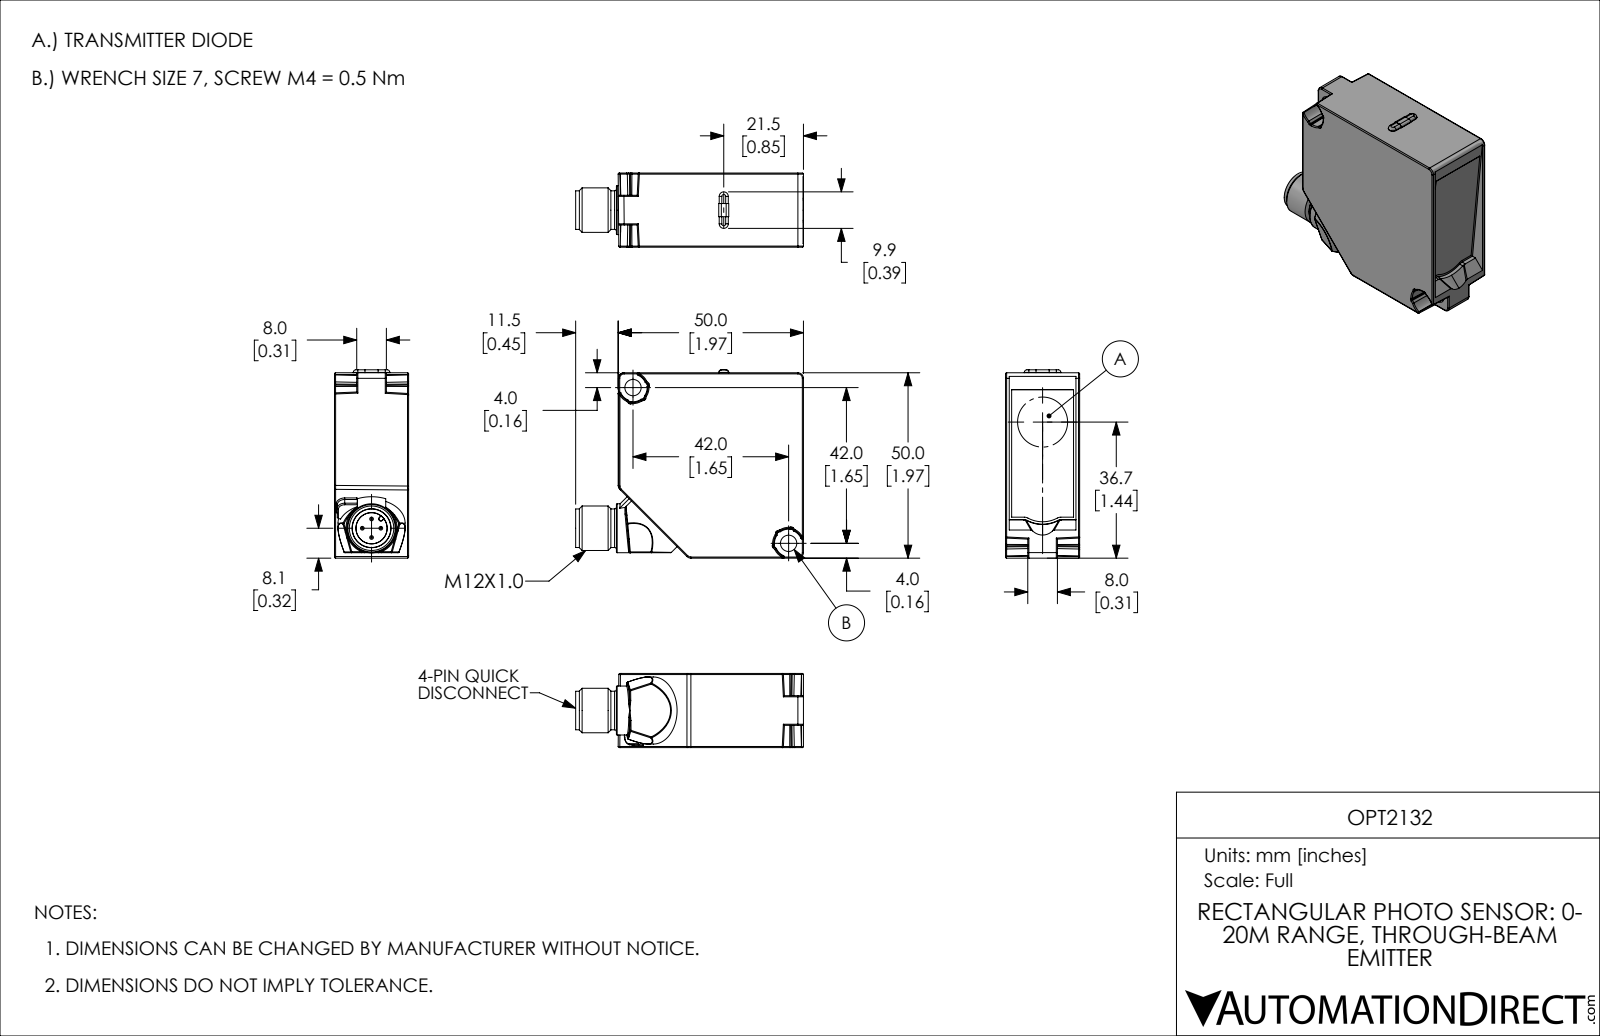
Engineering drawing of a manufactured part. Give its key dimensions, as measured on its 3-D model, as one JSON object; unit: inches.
{"part_name": "OPT2132", "step_written_by": "SolidWorks 2019 (AUTOMOTIVE_DESIGN)", "units": "inches", "bodies": {"solids": 2, "faces": 314, "planar": 94, "cylindrical": 107, "other": 113}, "overall_size": [2.42, 2, 0.787], "volume_in3": 2.818, "surface_area_in2": 16.38, "round_holes": [[0.173, 2], [0.713, 1]], "round_bosses_or_shafts": [[0.039, 4], [0.52, 1], [0.472, 1], [0.409, 1]], "partial_cylinders_radius": [[0.012, 63], [0.059, 5], [0.079, 5], [0.028, 4], [0.048, 2], [0.329, 1], [0.354, 1], [0.394, 1]], "face_to_face_distances": [0.787, 1.969, 0.039, 0.748, 0.236, 0.551, 0.197, 0.512, 0.058, 1.911], "hole_center_spacings": [2.339]}
